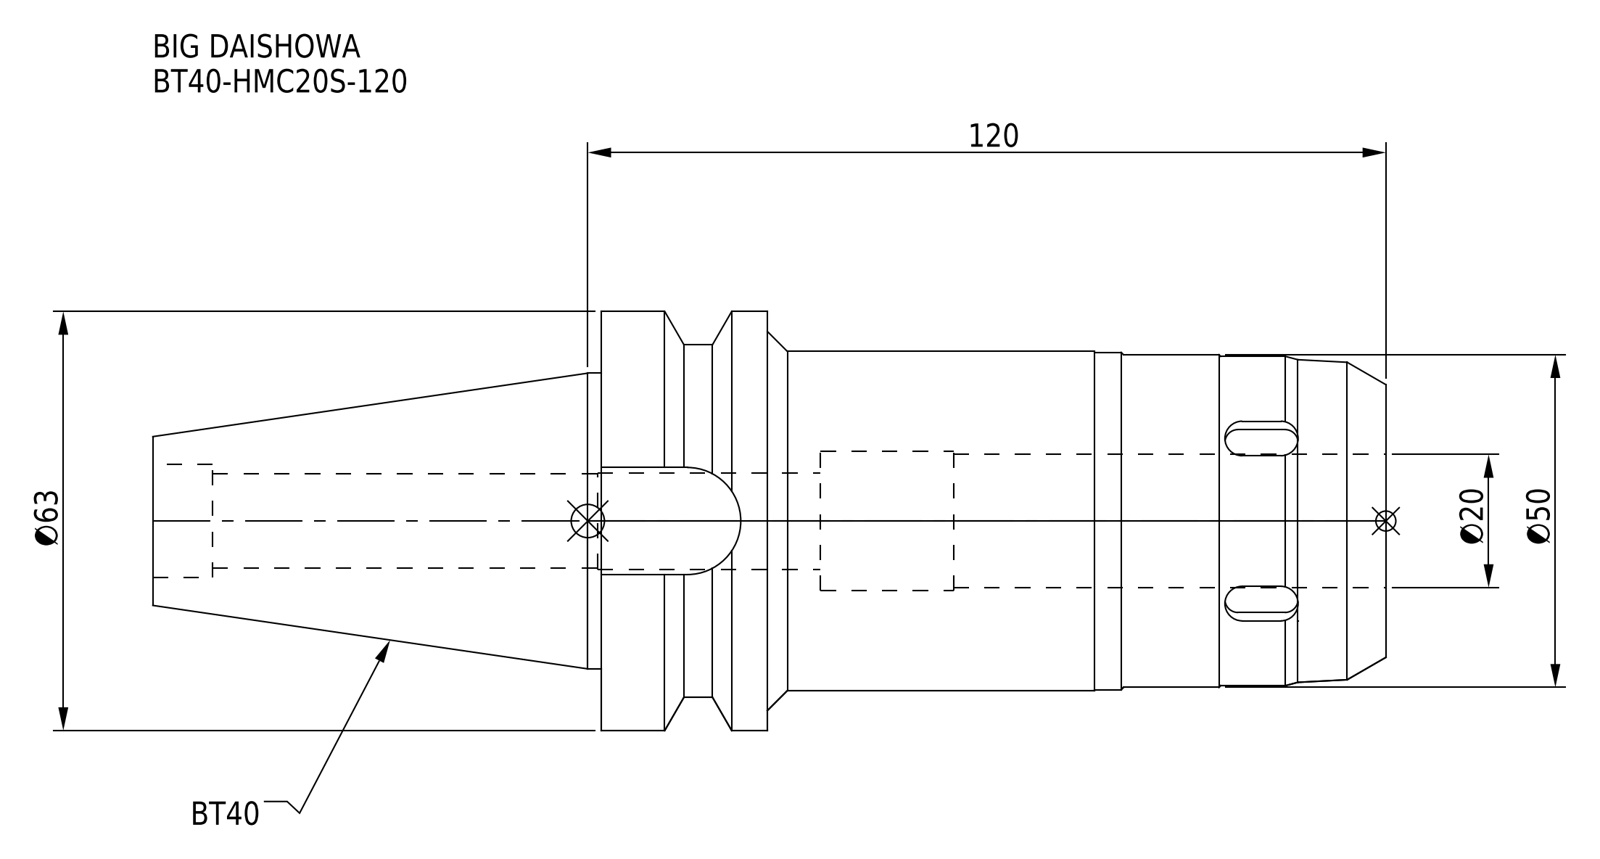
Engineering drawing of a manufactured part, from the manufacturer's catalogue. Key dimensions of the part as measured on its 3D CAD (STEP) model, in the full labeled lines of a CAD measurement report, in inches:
Part name (STEP PRODUCT): BT40-HMC20S-120
STEP written by: CREO PARAMETRIC BY PTC INC, 2016380 (AUTOMOTIVE_DESIGN)
Units: inches
Bodies: 1 solid, 95 faces (33 planar, 40 cylindrical, 22 other)
Overall size (bounding box): 7.299 × 2.48 × 2.48
Volume: 16.65 in³ · Surface area: 66.07 in²
Round holes (diameter × count): ⌀0.559 ×1, ⌀0.571 ×1, ⌀0.669 ×1, ⌀0.787 ×1, ⌀0.827 ×1
Round bosses / shafts (diameter × count): ⌀2.48 ×1, ⌀2.087 ×1, ⌀2.008 ×1, ⌀1.996 ×1, ⌀1.969 ×1, ⌀1.949 ×1, ⌀1.75 ×1
Partial cylindrical surfaces — rounded edges, fillets, slot ends (radius × count): R0.118 ×6, R0.317 ×1
Main face-to-face distances: 4.646, 3.661, 0.984, 1.772, 7.299, 3.638, 2.654, 0.634, 3.346, 0.315
